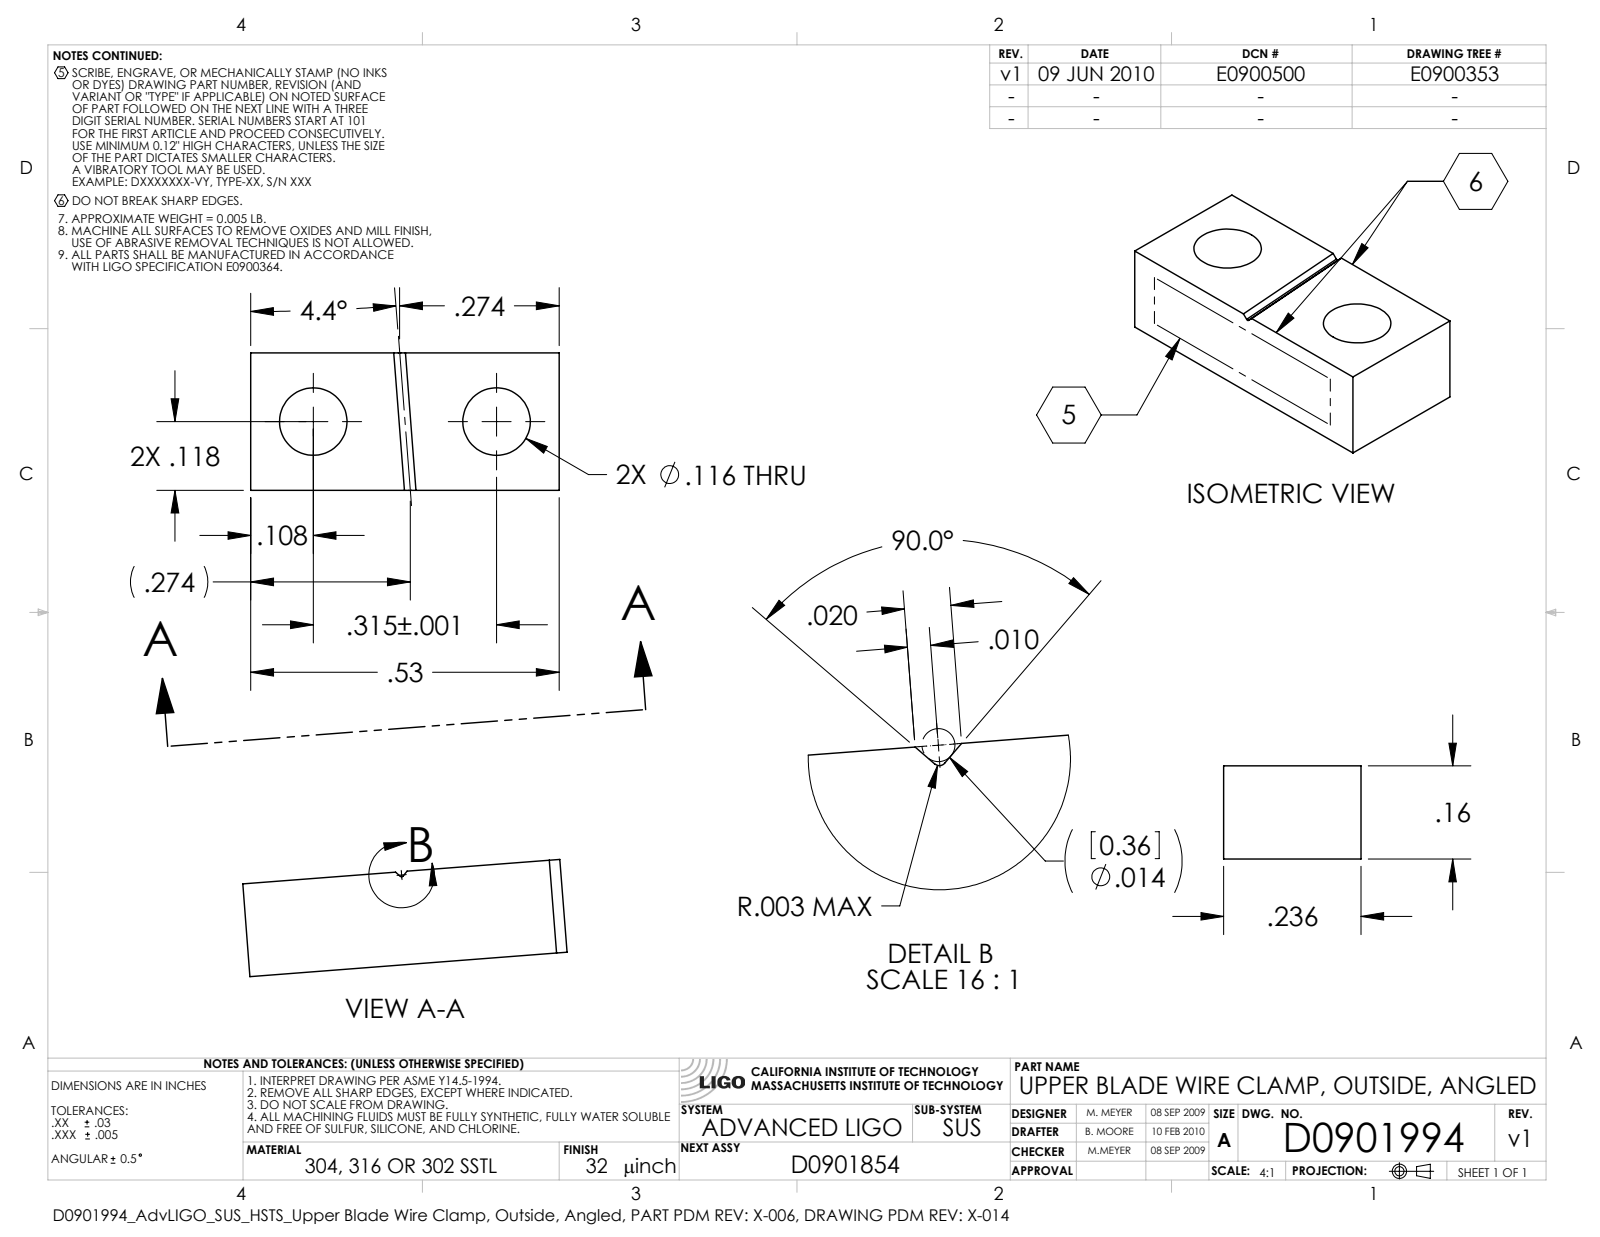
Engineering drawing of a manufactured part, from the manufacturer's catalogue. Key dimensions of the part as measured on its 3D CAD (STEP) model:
Part name (STEP PRODUCT): D0901994-v1_AdvLIGO_SUS_HSTS_Upper Blade Wire Clamp, Outside, Angled
STEP written by: SolidWorks 2009 (CONFIG_CONTROL_DESIGN)
Units: inches
Bodies: 1 solid, 14 faces (9 planar, 5 cylindrical, 0 other)
Overall size (bounding box): 0.53 × 0.236 × 0.16
Volume: 0.017 in³ · Surface area: 0.571 in²
Round holes (diameter × count): ⌀0.116 ×2
Main face-to-face distances: 0.16, 0.236, 0.53
Hole centre spacings: 0.315
